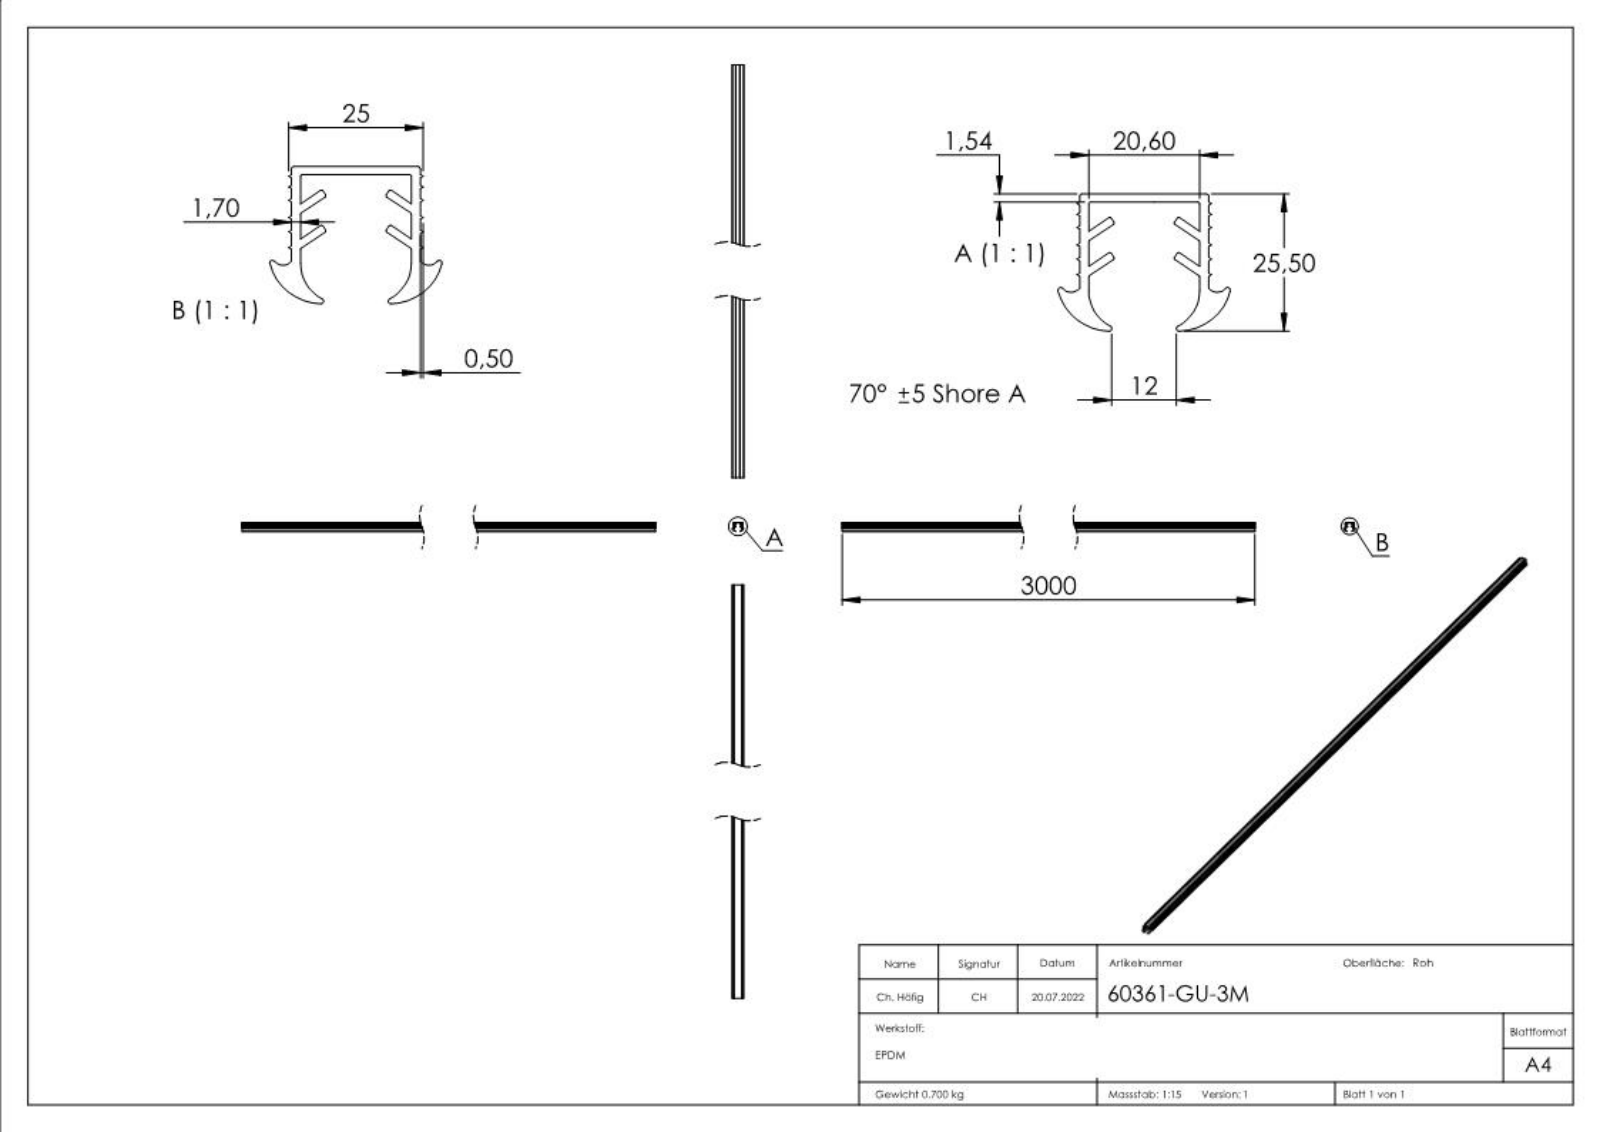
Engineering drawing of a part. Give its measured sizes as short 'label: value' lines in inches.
name: 60361-GU-3M
written by: SolidWorks 2018 (CONFIG_CONTROL_DESIGN)
unit: in
bodies: 1 solid, 374 faces (209 planar, 26 cylindrical, 139 other)
size: 118.11 × 1.26 × 1.004
volume: 36.19 in³; area: 992.8 in²
rounds: 14× R0.012, 6× R0.02, 2× R0.079, 2× R0.291, 2× R0.394
face distances: 0.067, 0.878, 0.061, 0.945, 0.811, 0.213, 0.059, 0.154, 0.059, 0.213
